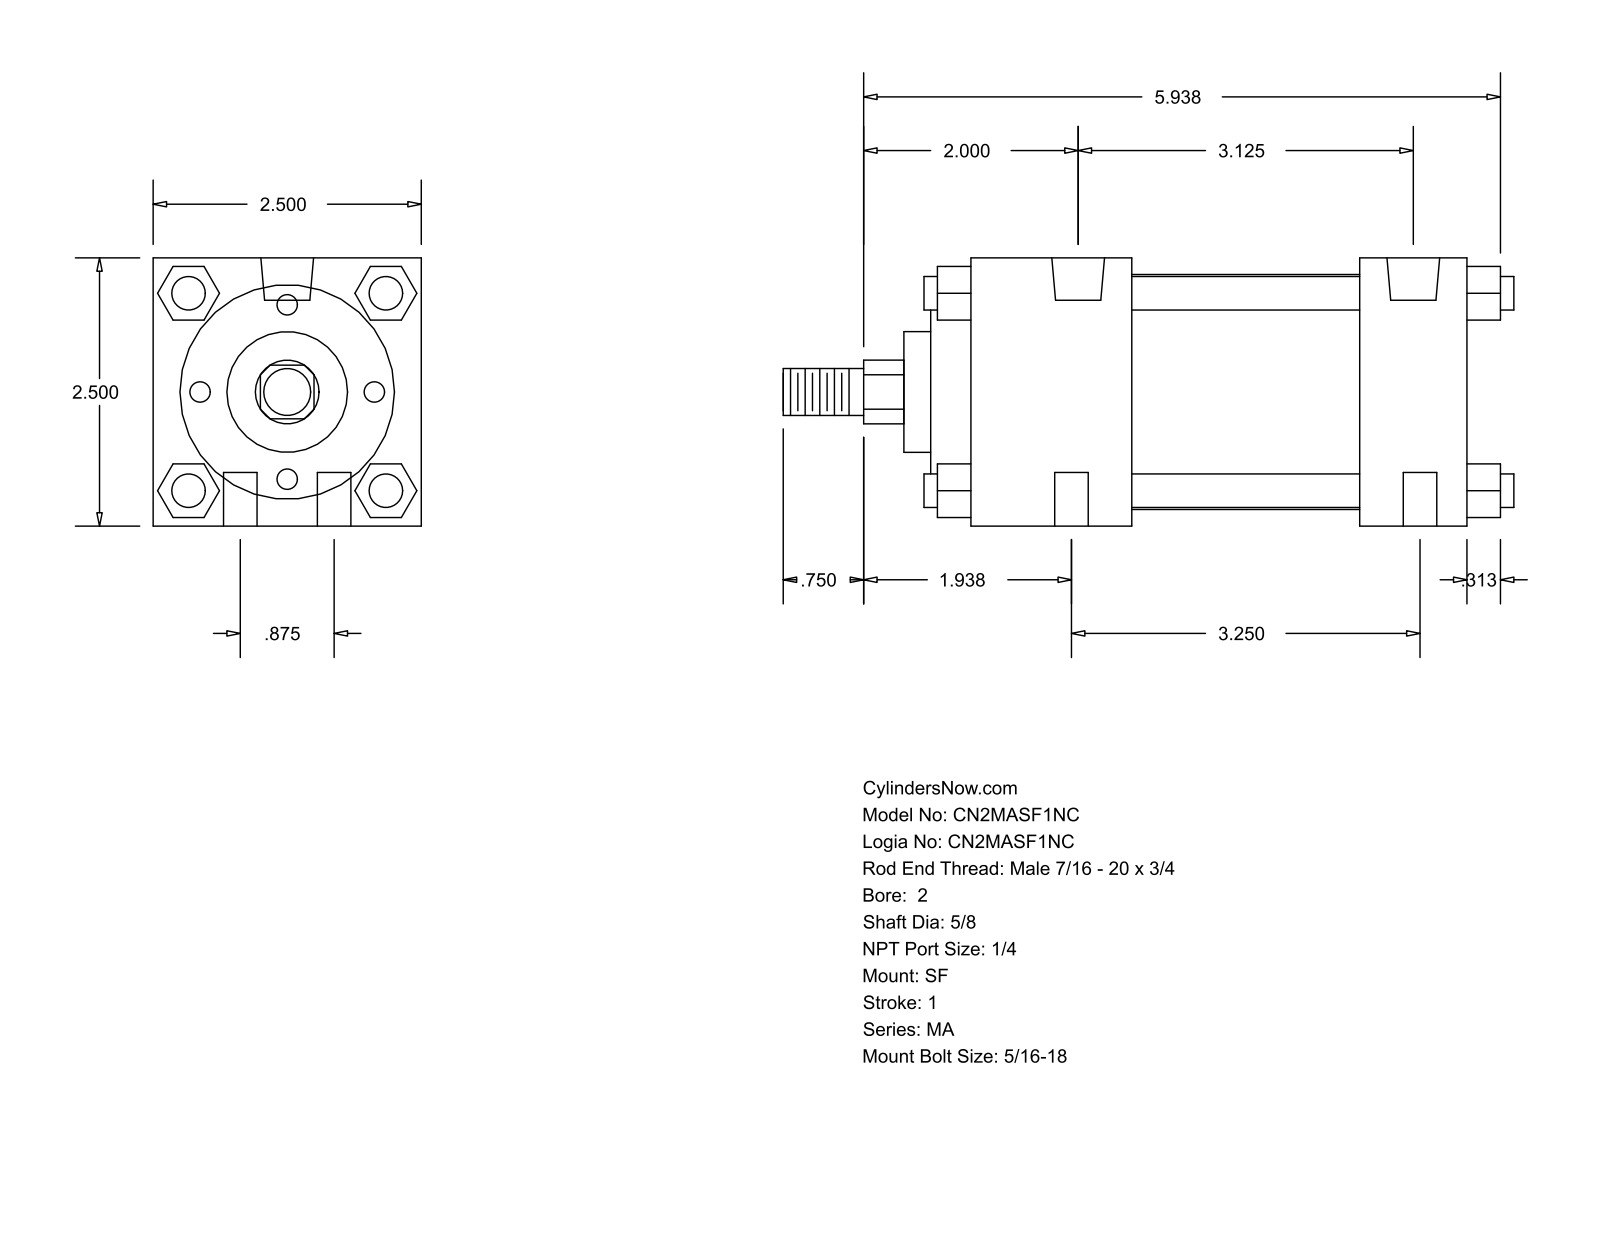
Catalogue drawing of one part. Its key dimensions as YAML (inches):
part_name: "MA_SF__0200_0.625"
step_written_by: "GSSL Pune (CONFIG_CONTROL_DESIGN)"
units: inches
bodies: {solids: 0, faces: 126, planar: 95, cylindrical: 31, other: 0}
overall_size: [6.813, 2.5, 2.5]
round_holes:
  - {diameter: 0.313, count: 6}
  - {diameter: 0.492, count: 2}
round_bosses_or_shafts:
  - {diameter: 0.313, count: 4}
  - {diameter: 2.19, count: 1}
  - {diameter: 2, count: 1}
  - {diameter: 1.125, count: 1}
  - {diameter: 0.625, count: 1}
  - {diameter: 0.437, count: 1}
partial_cylinders:
  - {radius: 0.297, count: 1}
face_to_face_distances: [2.5, 2.125, 0.5, 1.5, 4.625, 3.625, 1, 3.125, 0.375, 1.875]
hole_center_spacings: [0.442, 0.875, 3.125, 3.217, 3.218, 3.25, 3.366]
